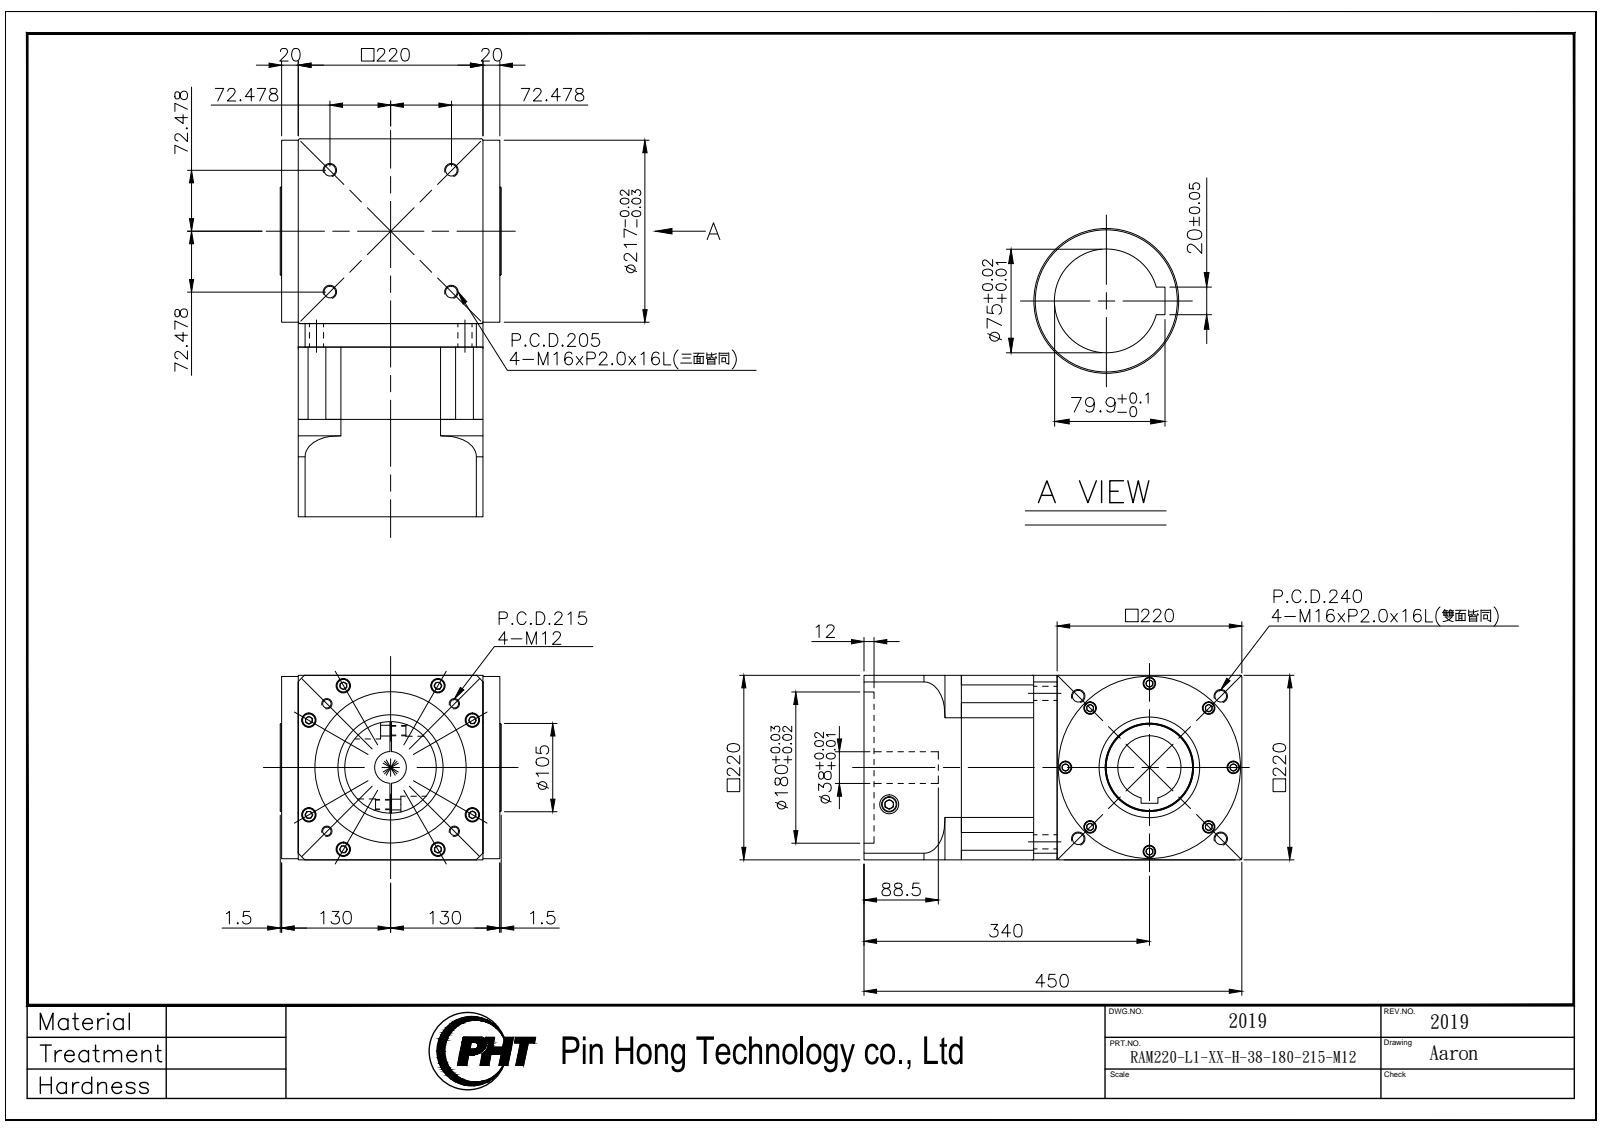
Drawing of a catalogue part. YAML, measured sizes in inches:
part_name: "RAM220-L1-XX-H-38-180-215-M12_2019"
step_written_by: "SolidWorks 2016 (AUTOMOTIVE_DESIGN)"
units: inches
bodies: {solids: 4, faces: 946, planar: 442, cylindrical: 316, other: 188}
overall_size: [17.717, 10.354, 8.661]
volume: 1277
surface_area: 1629
round_holes:
  - {diameter: 0.354, count: 12}
  - {diameter: 0.551, count: 12}
  - {diameter: 0.591, count: 12}
  - {diameter: 0.669, count: 12}
  - {diameter: 0.433, count: 8}
  - {diameter: 0.402, count: 4}
  - {diameter: 0.886, count: 2}
  - {diameter: 1.496, count: 1}
  - {diameter: 2.953, count: 1}
  - {diameter: 2.992, count: 1}
  - {diameter: 4.921, count: 1}
  - {diameter: 7.087, count: 1}
round_bosses_or_shafts:
  - {diameter: 0.512, count: 12}
  - {diameter: 0.63, count: 8}
  - {diameter: 0.945, count: 4}
  - {diameter: 8.543, count: 1}
  - {diameter: 4.724, count: 1}
  - {diameter: 4.291, count: 1}
  - {diameter: 4.134, count: 1}
partial_cylinders:
  - {radius: 0.591, count: 4}
  - {radius: 4.921, count: 1}
  - {radius: 5.906, count: 1}
face_to_face_distances: [8.661, 3.386, 4.488, 1.102, 0.787, 13.15, 9.764, 9.449, 5.079, 1.693]
hole_center_spacings: [3.937, 2.038, 4.429, 5.568, 6.819, 7.606, 1.147, 1.172]
